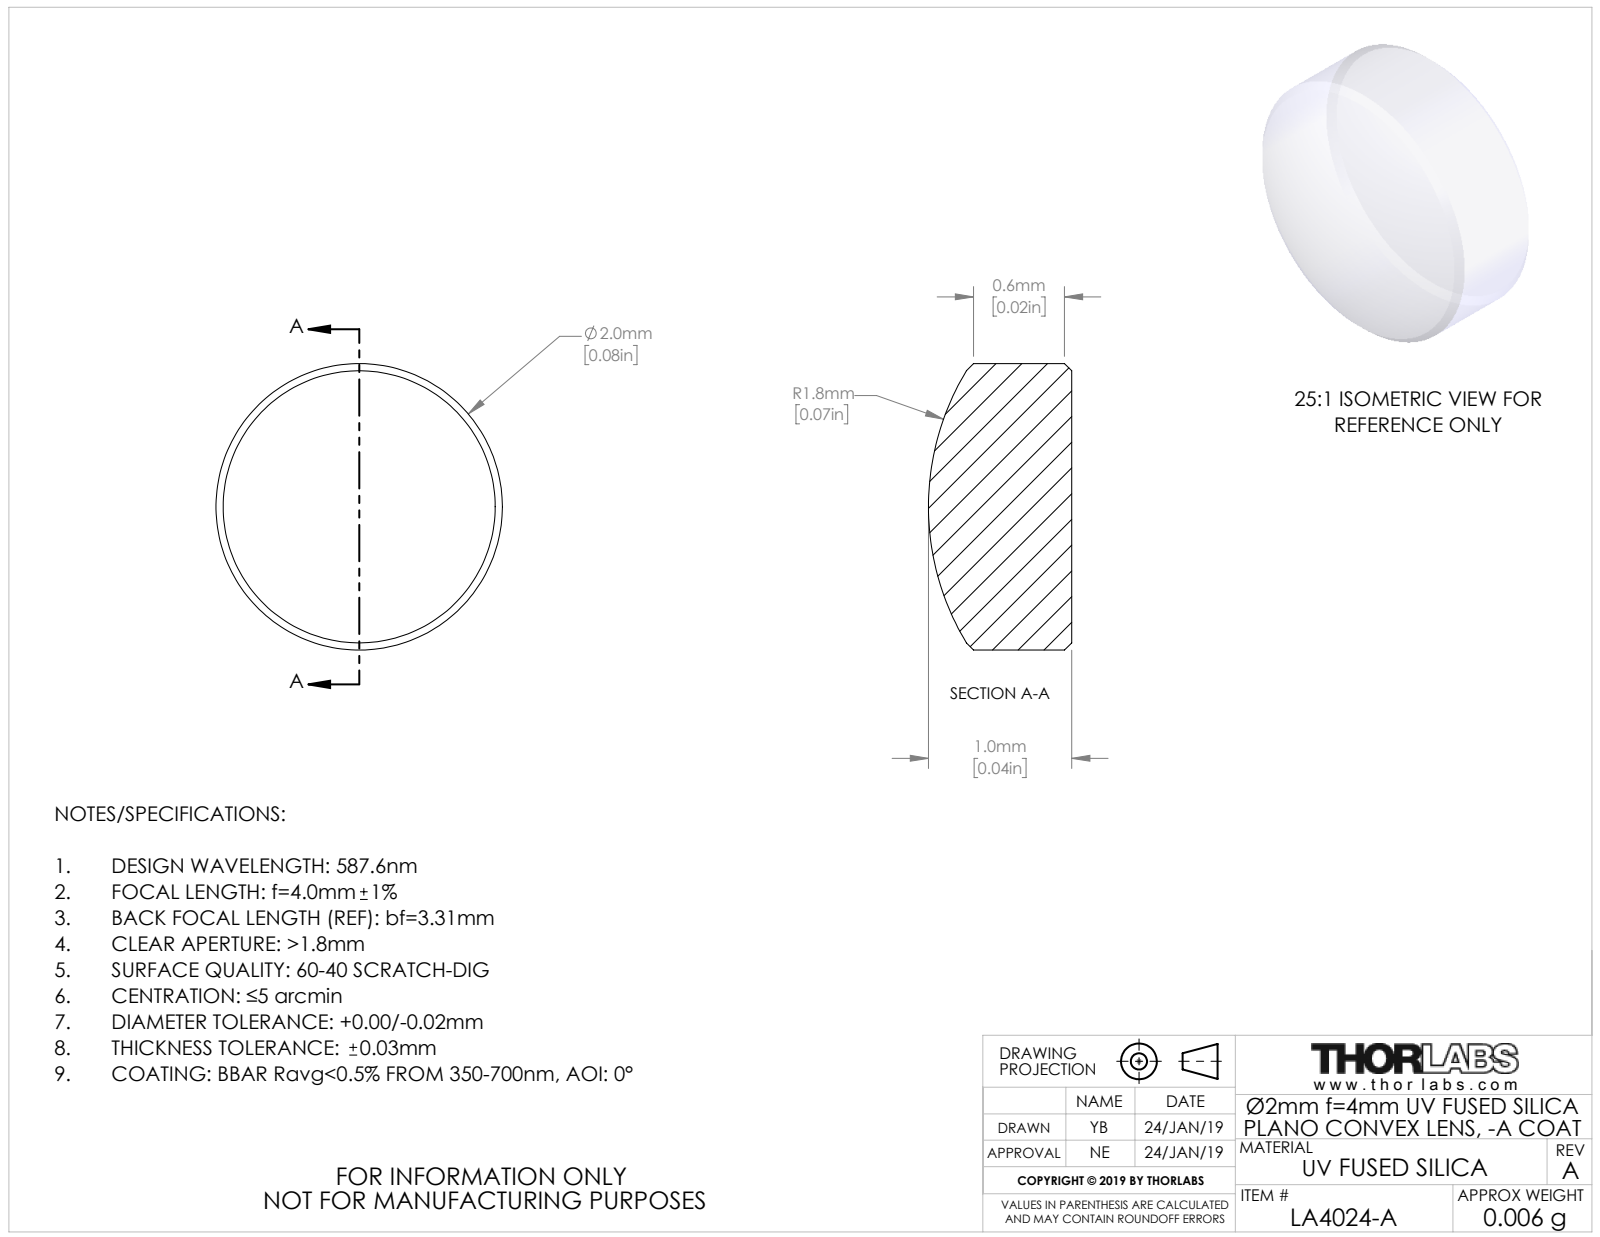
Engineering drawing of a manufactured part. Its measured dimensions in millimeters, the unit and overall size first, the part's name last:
Units: millimetres
Overall size (bounding box): 2 × 2 × 1
Round bosses / shafts (diameter × count): ⌀2 ×1
Volume: 3 mm³ · Surface area: 11 mm²
Bodies: 1 solid, 9 faces (1 planar, 2 cylindrical, 6 other)
Part name (STEP PRODUCT): TTN162803-E0W
STEP written by: SolidWorks 2018 (CONFIG_CONTROL_DESIGN)
